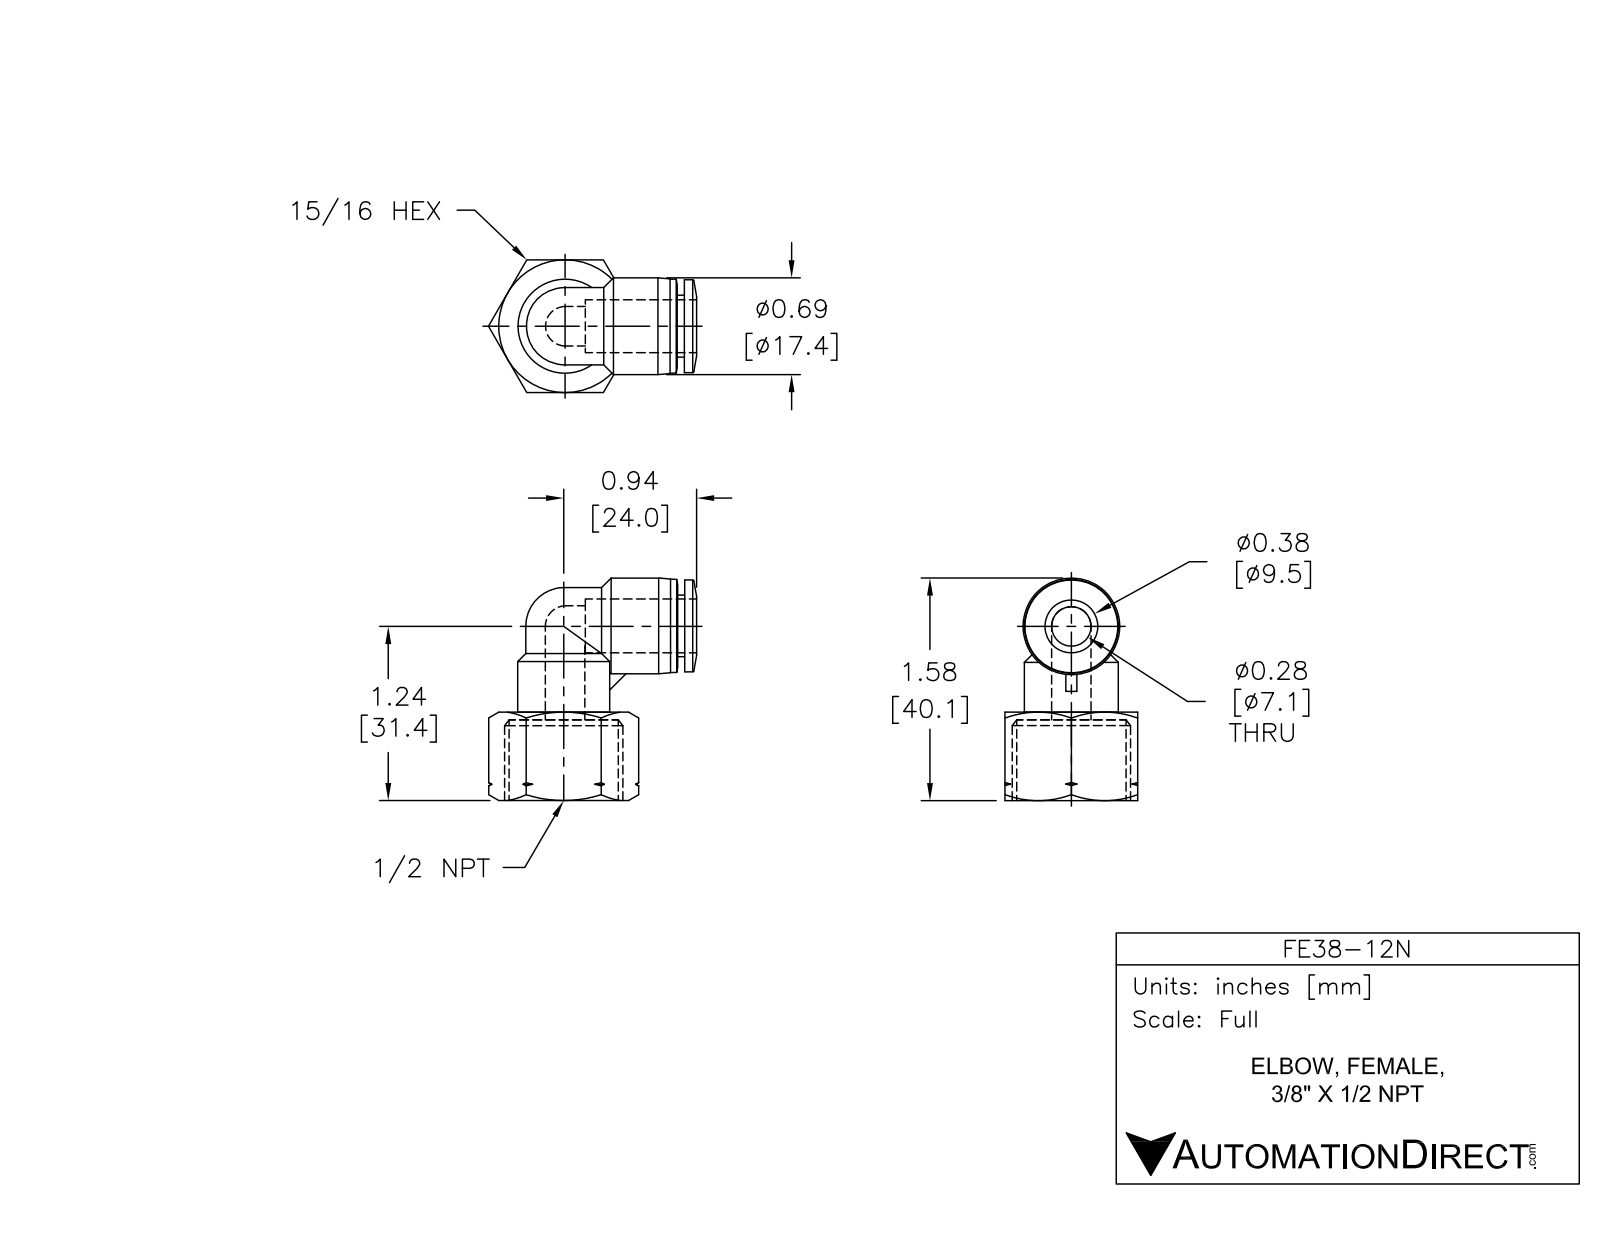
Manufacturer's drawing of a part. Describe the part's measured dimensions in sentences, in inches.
The part is named "FE38-12N". Its 3-D file was written by "SolidWorks 2015 (AUTOMOTIVE_DESIGN)". It is 1 solid with 85 faces: 16 planar, 20 cylindrical and 49 other. Overall it measures 1.585 by 1.512 by 0.945 inches. Its volume is 0.523 cubic inches and its surface area 9.939 square inches. Round holes: 2 of diameter 0.276, 1 of diameter 0.386. Round bosses or shafts: 2 of diameter 0.669, 1 of diameter 0.689, 1 of diameter 0.661, 1 of diameter 0.551, 1 of diameter 0.441. Partial cylindrical surfaces (rounded edges, fillets, slot ends): 1 of radius 0.276. The main face-to-face distances are 0.945, 0.059, 0.571, 0.63, 0.051, 0.654, 0.705, 0.433, 0.512, 0.079.
